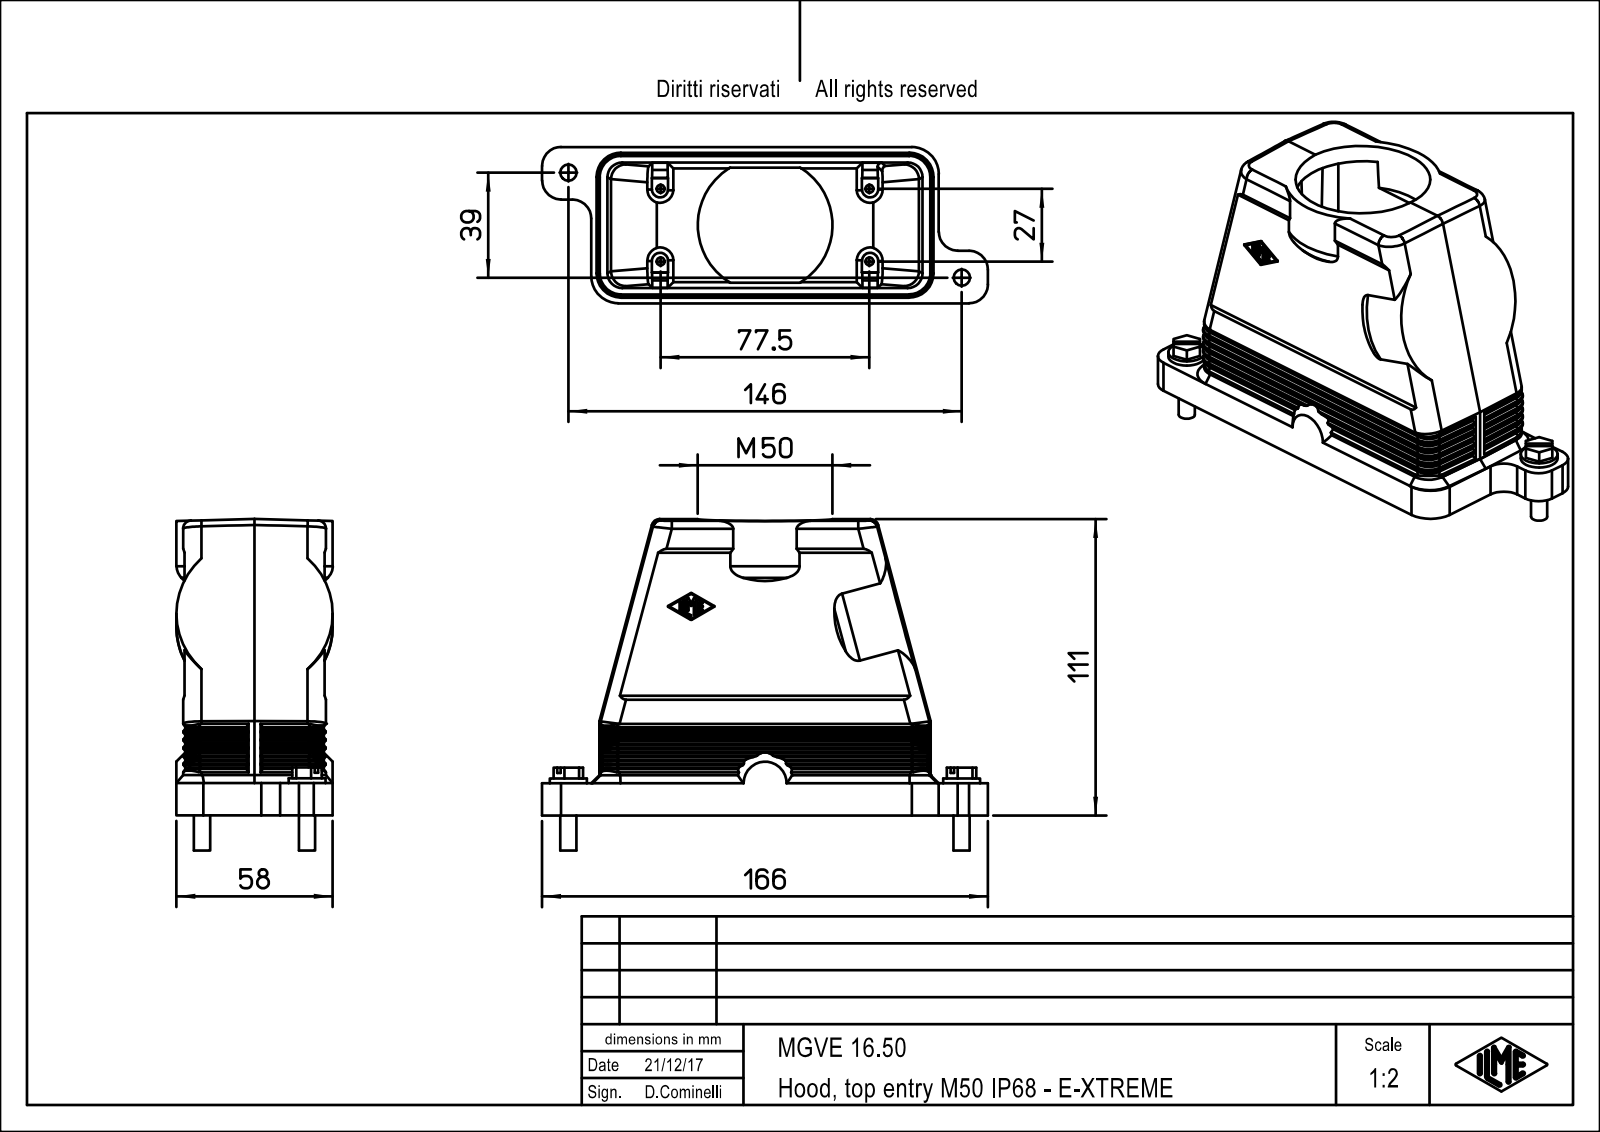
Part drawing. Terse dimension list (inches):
name: MGVE_16.50
written by: PTC Creo Elements/Direct Modeling 19.0E 27-Jun-2016 (C) Parametric Technology GmbH (AUTOMOTIVE_DESIGN)
unit: in
bodies: 1 solid, 537 faces (257 planar, 124 cylindrical, 156 other)
size: 6.516 × 4.843 × 2.283
volume: 10.79 in³; area: 128.9 in²
holes: 4× ⌀0.118, 1× ⌀1.969
bosses: 2× ⌀0.539, 2× ⌀0.236
rounds: 62× R0.276, 15× R0.013, 8× R0.217, 4× R0.335, 2× R0.007, 2× R0.394, 2× R1.142, 1× R0.007
face distances: 2.047, 0.118, 2.165, 0.098, 0.02, 2.185, 2.067, 3.071, 0.131, 0.066
hole spacings: 1.615, 1.063, 3.051, 3.231
